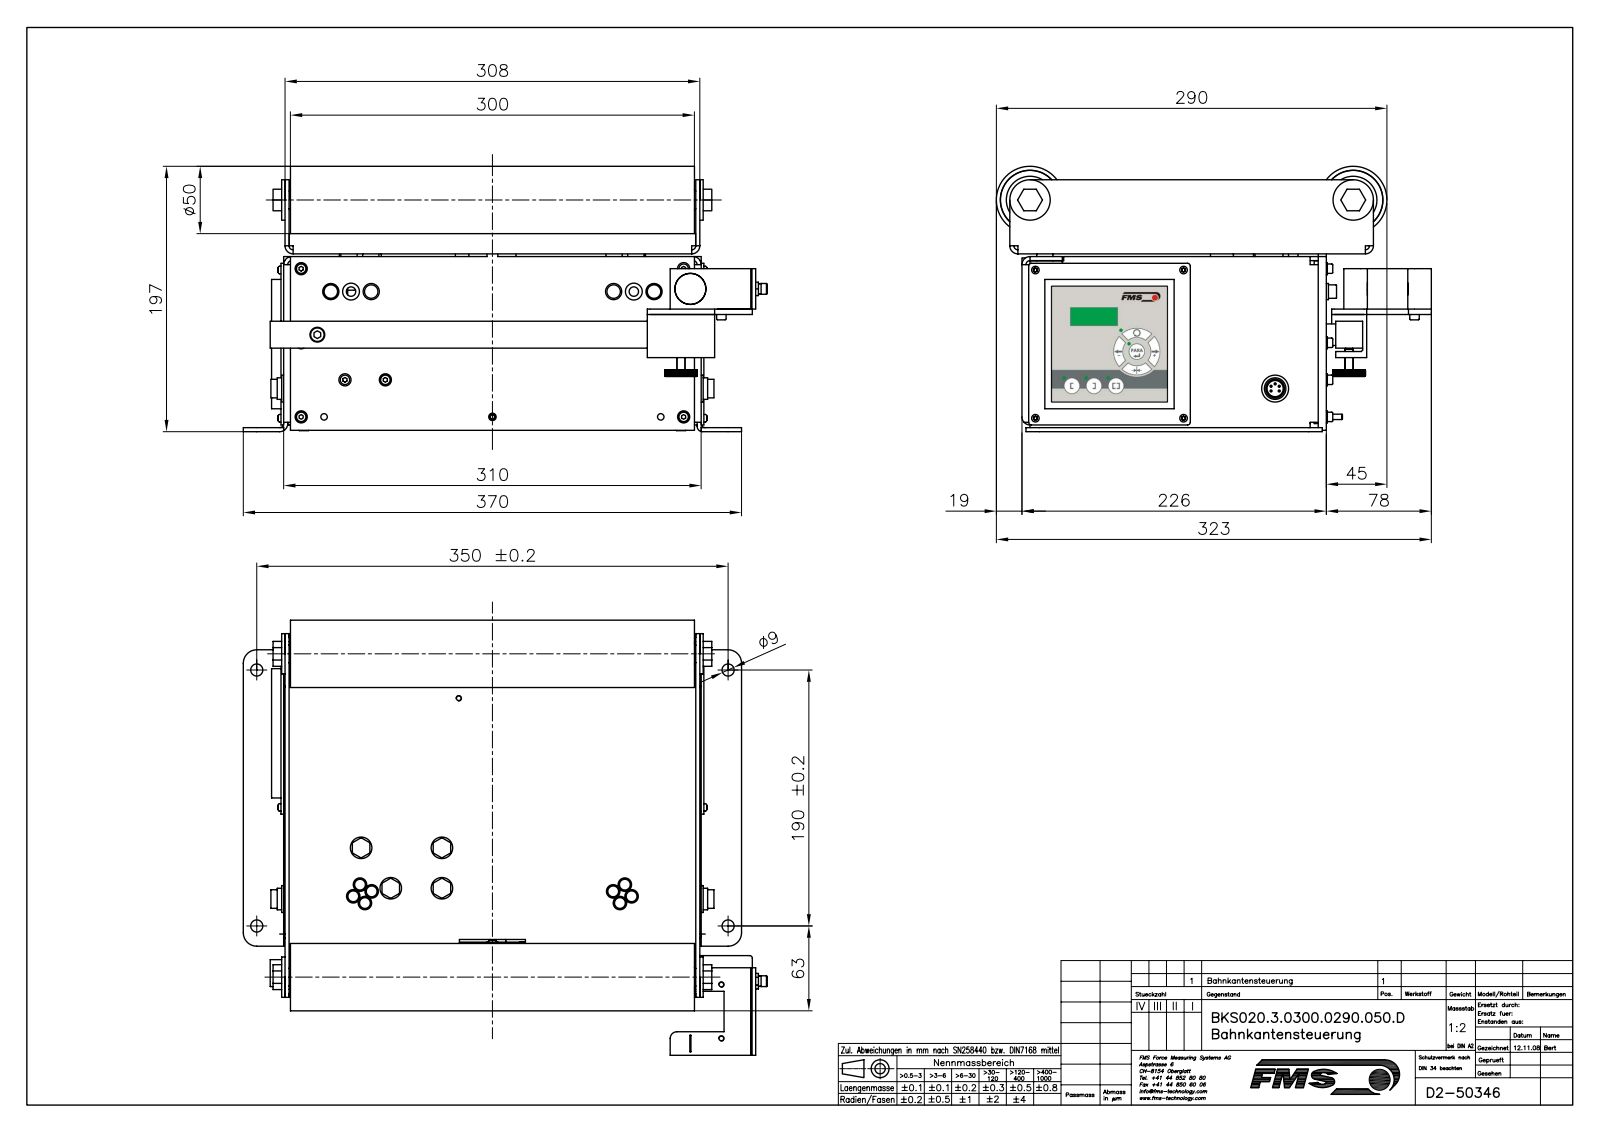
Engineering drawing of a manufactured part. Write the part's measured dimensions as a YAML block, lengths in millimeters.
part_name: "K50346; K49778; K49776; TEIL1 (+8 more)"
step_written_by: "Mechanical Desktop 2007 (CONFIG_CONTROL_DESIGN)"
units: millimeters
bodies: {solids: 150, faces: 4293, planar: 2313, cylindrical: 1558, other: 422}
overall_size: [389.1, 323, 197]
volume: 2177000
surface_area: 1297000
round_holes:
  - {diameter: 4.3, count: 14}
  - {diameter: 3.42, count: 13}
  - {diameter: 2.2, count: 8}
  - {diameter: 2.6, count: 8}
  - {diameter: 3.2, count: 8}
  - {diameter: 5.3, count: 8}
  - {diameter: 6.4, count: 8}
  - {diameter: 6, count: 6}
  - {diameter: 8.4, count: 6}
  - {diameter: 3.5, count: 4}
  - {diameter: 4.8, count: 4}
  - {diameter: 7, count: 3}
round_bosses_or_shafts:
  - {diameter: 10, count: 18}
  - {diameter: 4, count: 18}
  - {diameter: 8, count: 15}
  - {diameter: 6, count: 11}
  - {diameter: 7, count: 10}
  - {diameter: 12, count: 8}
  - {diameter: 9, count: 8}
  - {diameter: 5, count: 8}
partial_cylinders:
  - {radius: 0.32, count: 48}
  - {radius: 2, count: 24}
  - {radius: 1, count: 19}
  - {radius: 3, count: 14}
  - {radius: 6, count: 13}
  - {radius: 5, count: 10}
  - {radius: 3.15, count: 8}
  - {radius: 8, count: 8}
face_to_face_distances: [3, 1, 2, 127, 5, 6, 130, 128, 131, 4]
hole_center_spacings: [10, 83.5, 97.44, 97.87, 110, 15, 30, 198.06]
